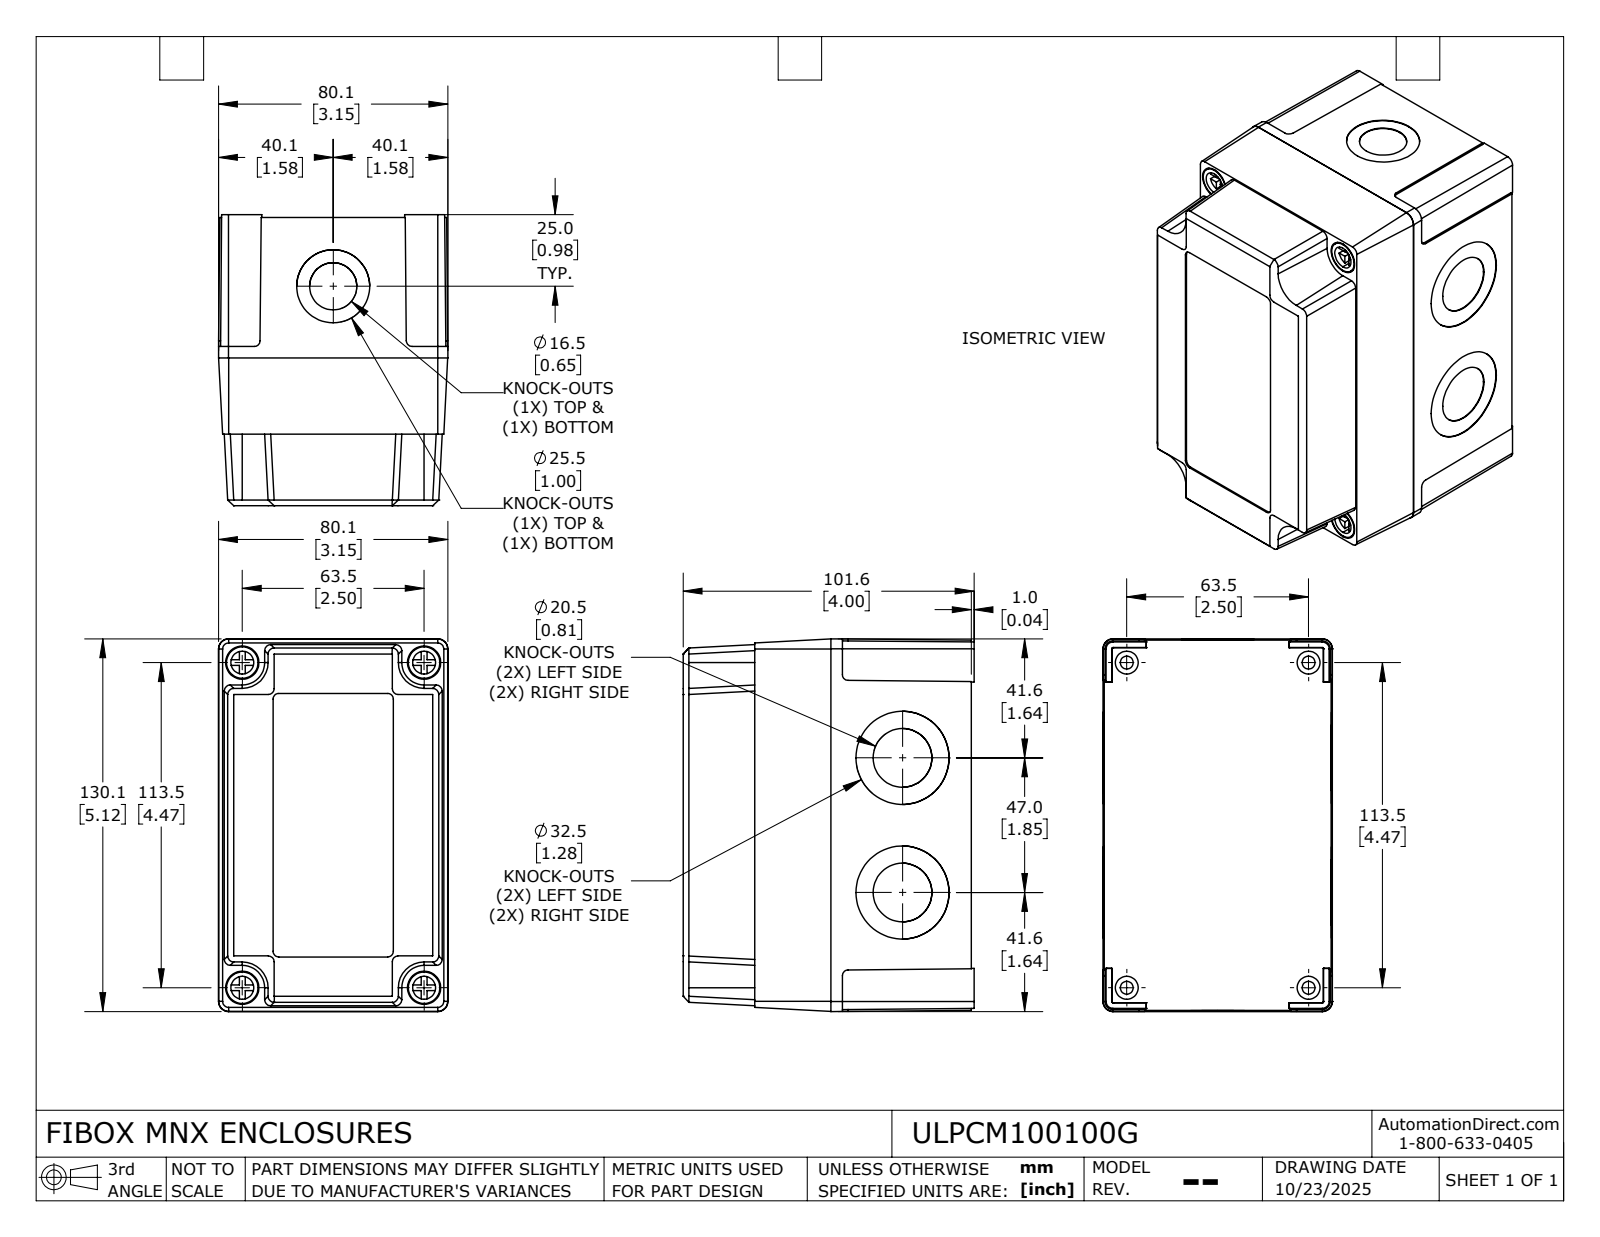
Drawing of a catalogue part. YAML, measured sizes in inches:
part_name: "ULPCM100100G_Default"
step_written_by: "SolidWorks 2024 (CONFIG_CONTROL_DESIGN)"
units: inches
bodies: {solids: 6, faces: 557, planar: 327, cylindrical: 184, other: 46}
overall_size: [5.122, 4, 3.154]
volume: 12.47
surface_area: 204.4
round_holes:
  - {diameter: 0.126, count: 8}
  - {diameter: 0.157, count: 8}
  - {diameter: 0.177, count: 4}
  - {diameter: 0.315, count: 4}
  - {diameter: 0.457, count: 4}
  - {diameter: 0.807, count: 4}
  - {diameter: 1.28, count: 4}
  - {diameter: 0.65, count: 2}
  - {diameter: 1.004, count: 2}
round_bosses_or_shafts:
  - {diameter: 0.315, count: 8}
  - {diameter: 0.098, count: 8}
  - {diameter: 0.433, count: 4}
  - {diameter: 0.283, count: 4}
partial_cylinders:
  - {radius: 0.079, count: 8}
  - {radius: 0.083, count: 8}
  - {radius: 0.056, count: 6}
  - {radius: 0.021, count: 4}
  - {radius: 0.197, count: 4}
  - {radius: 0.023, count: 2}
face_to_face_distances: [0.165, 3.87, 0.118, 3.752, 0.055, 0.077, 0.022, 0.026, 0.139, 1.811]
hole_center_spacings: [0.841, 0.888, 1.333, 1.476, 1.939, 2.159, 2.174, 2.281]
